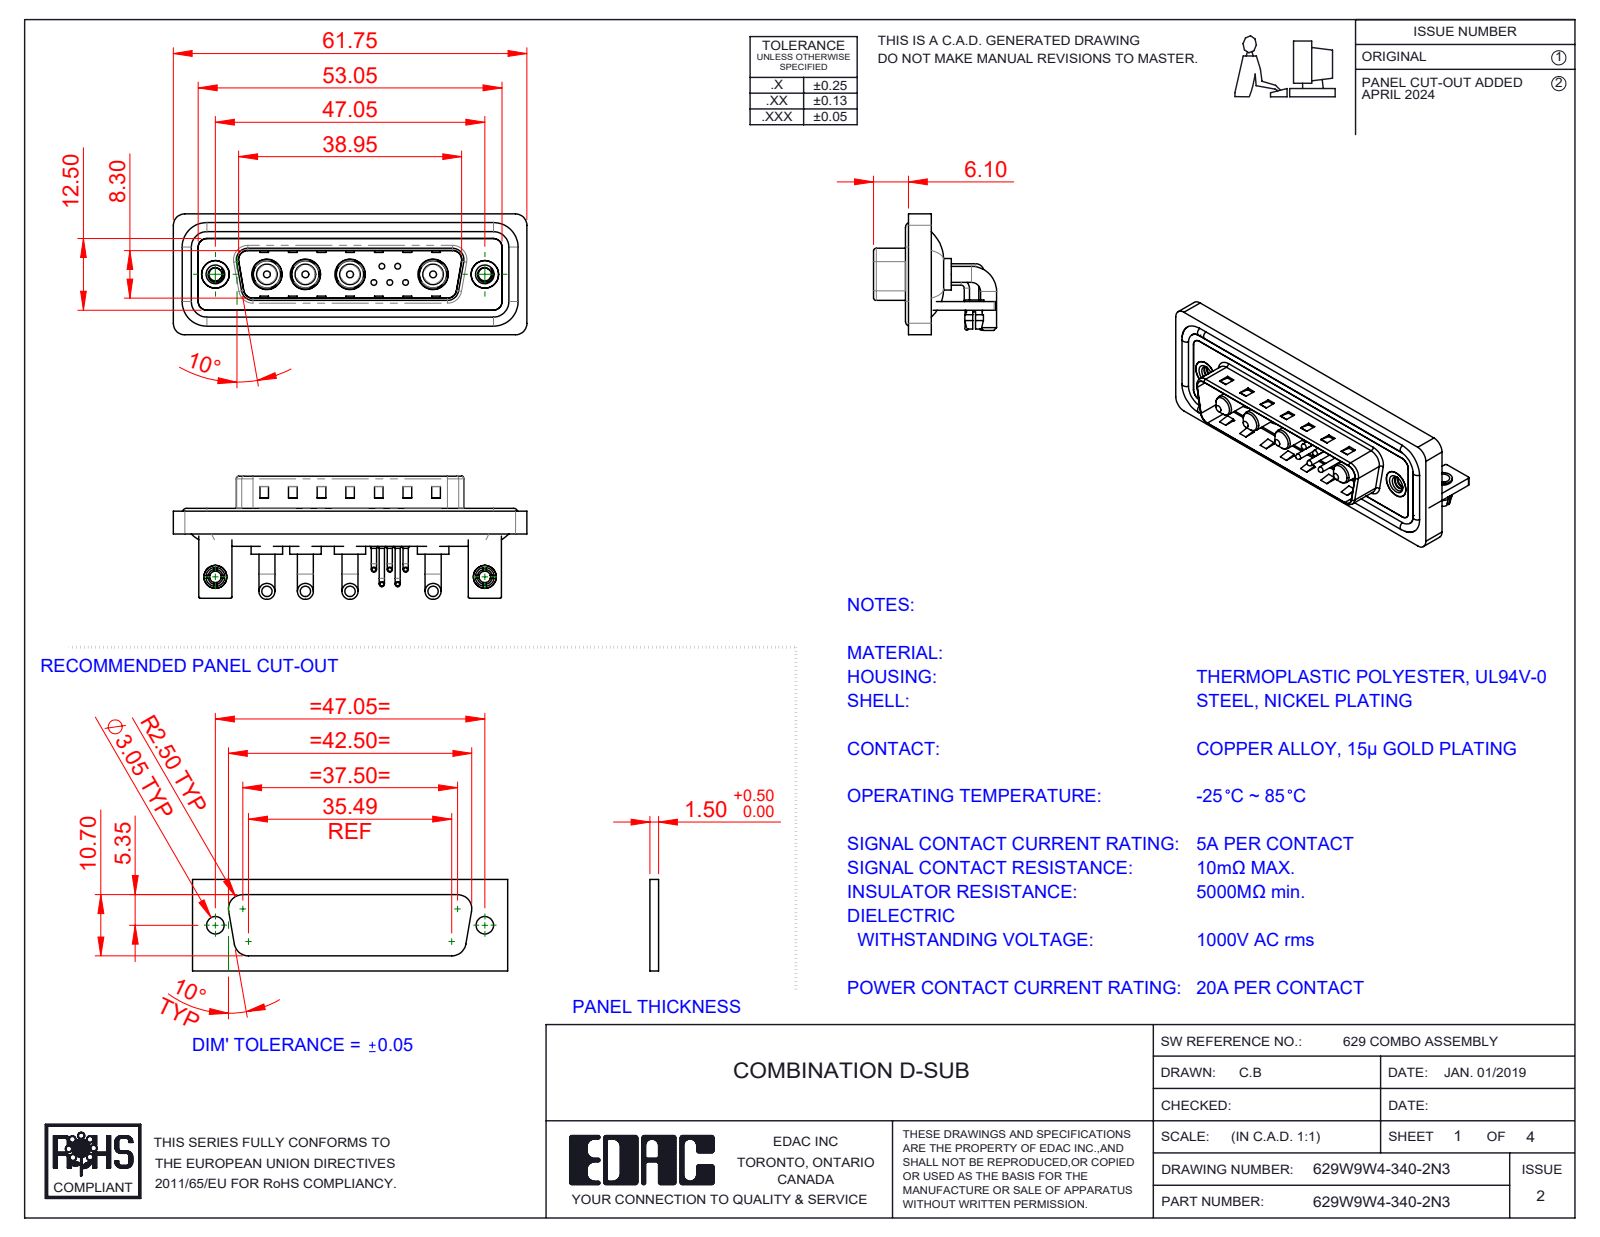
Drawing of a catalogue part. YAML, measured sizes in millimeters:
part_name: "629Combo Waterproof Housing_25 Contacts; 629Combo Contact Row 2; 629Combo Contact Row 1; 629Combo Housing_9W4 (+7 more)"
step_written_by: "SolidWorks 2023 (CONFIG_CONTROL_DESIGN)"
units: millimeters
bodies: {solids: 24, faces: 1337, planar: 637, cylindrical: 502, other: 198}
overall_size: [61.75, 21.5, 21.1]
volume: 8018
surface_area: 13174
round_holes:
  - {diameter: 2, count: 7}
  - {diameter: 0.75, count: 5}
  - {diameter: 1.6, count: 5}
  - {diameter: 4.85, count: 4}
  - {diameter: 5.3, count: 4}
  - {diameter: 2.26, count: 2}
  - {diameter: 2.5, count: 2}
  - {diameter: 3.2, count: 2}
  - {diameter: 4, count: 2}
  - {diameter: 4.8, count: 2}
  - {diameter: 5, count: 2}
round_bosses_or_shafts:
  - {diameter: 0.9, count: 10}
  - {diameter: 2.8, count: 8}
  - {diameter: 1.5, count: 5}
  - {diameter: 1, count: 5}
  - {diameter: 0.65, count: 5}
  - {diameter: 5.5, count: 4}
  - {diameter: 5.2, count: 4}
  - {diameter: 4.75, count: 4}
partial_cylinders:
  - {radius: 2, count: 19}
  - {radius: 1.5, count: 18}
  - {radius: 0.25, count: 16}
  - {radius: 0.5, count: 9}
  - {radius: 1.6, count: 8}
  - {radius: 1.01, count: 5}
  - {radius: 0.6, count: 4}
  - {radius: 0.65, count: 4}
face_to_face_distances: [0.4, 1.5, 0.8, 2.9, 2.1, 1.1, 3.7, 4.1, 4.5, 1.6]
hole_center_spacings: [3.16, 2.77, 5.04, 14.5, 47.05, 2.78, 4.4, 4.41]
